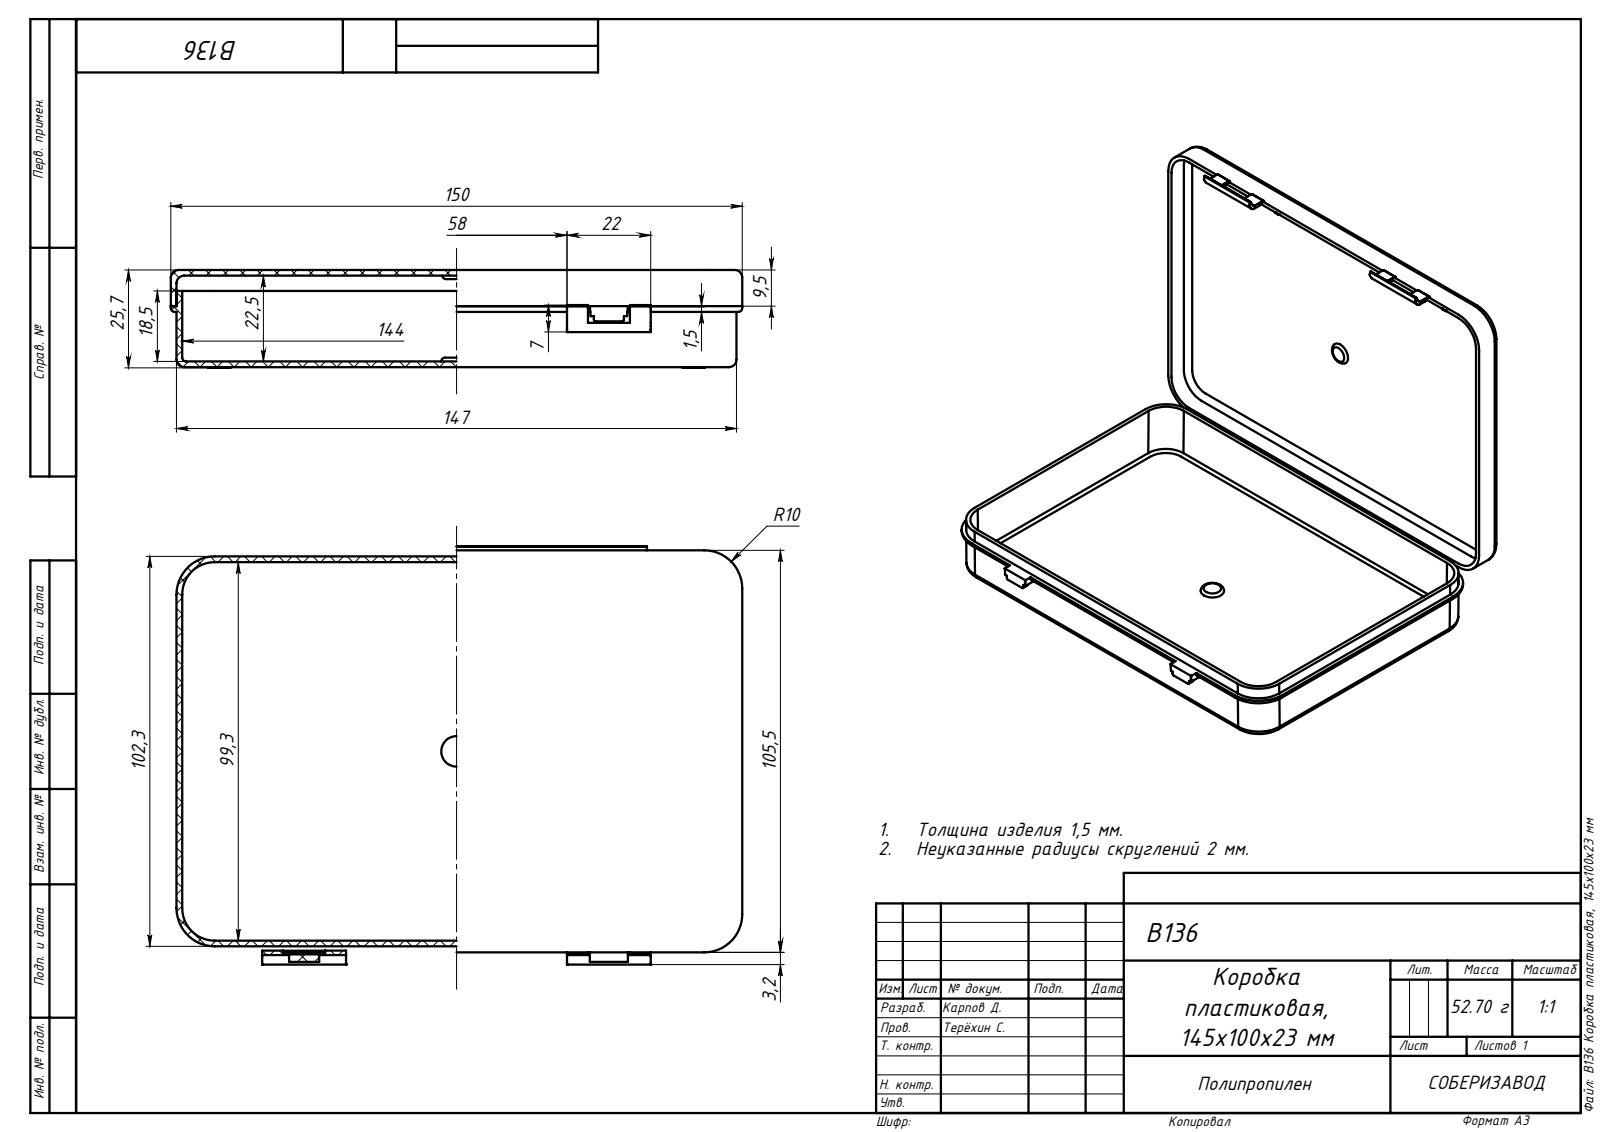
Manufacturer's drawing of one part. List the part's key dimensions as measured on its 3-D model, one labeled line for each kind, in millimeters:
Part name (STEP PRODUCT): B136 Емкость; B136 Защелка; B136 Крышка; B136 Коробка пластиковая, 145x100x23 мм
STEP written by: SolidWorks 2020 (AUTOMOTIVE_DESIGN)
Units: millimetres
Bodies: 4 solids, 284 faces (158 planar, 86 cylindrical, 40 other)
Overall size (bounding box): 150 × 109.7 × 25.7
Volume: 66 406 mm³ · Surface area: 90 381 mm²
Partial cylindrical surfaces — rounded edges, fillets, slot ends (radius × count): R2 ×12, R0.5 ×10, R1 ×8, R8.5 ×8, R10 ×8, R0.1 ×6, R0.23 ×1, R0.9 ×1
Main face-to-face distances: 1.5, 24, 25.5, 22.5, 147, 145.5, 9.5, 14.5, 104, 16
